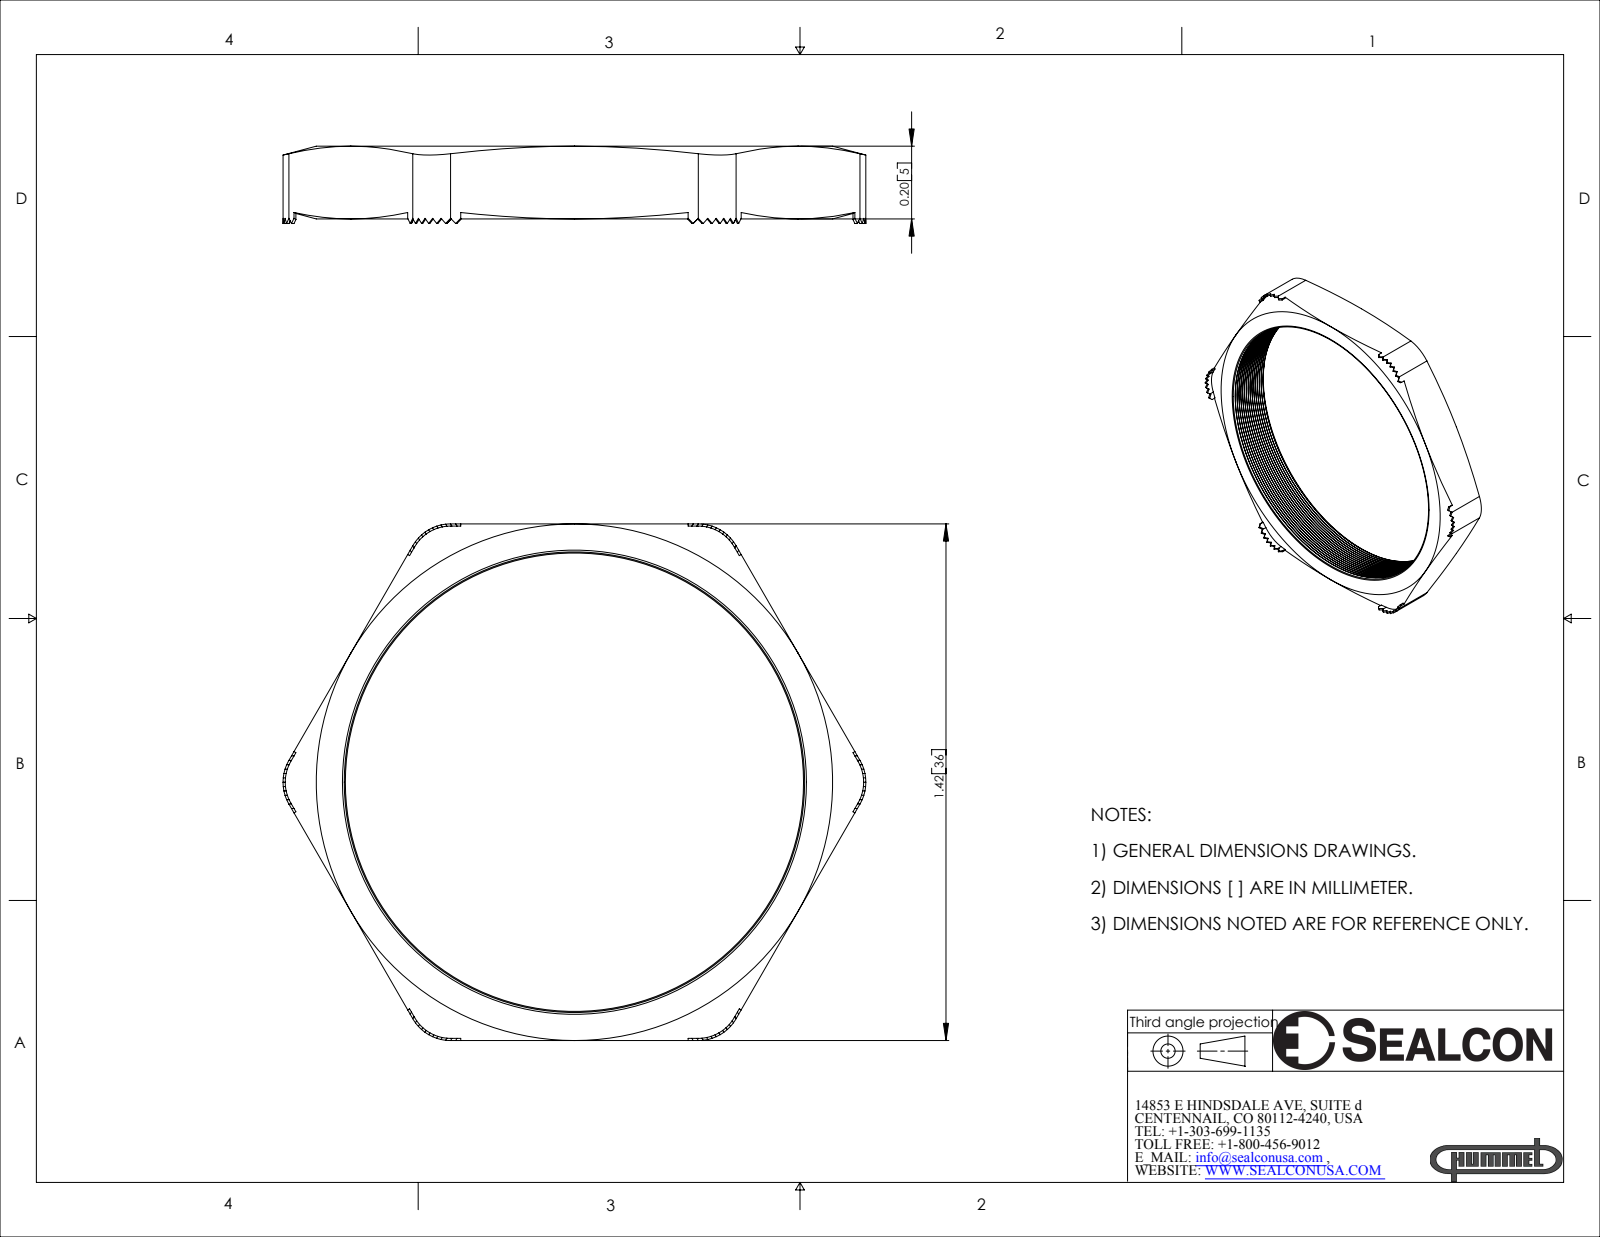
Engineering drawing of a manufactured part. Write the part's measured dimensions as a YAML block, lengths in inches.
part_name: "NM-32-BE"
step_written_by: "SolidWorks 2007 (CONFIG_CONTROL_DESIGN)"
units: inches
bodies: {solids: 1, faces: 248, planar: 116, cylindrical: 46, other: 86}
overall_size: [1.603, 1.42, 0.213]
volume: 0.093
surface_area: 3.454
round_holes:
  - {diameter: 1.26, count: 1}
partial_cylinders:
  - {radius: 0.114, count: 6}
  - {radius: 0.12, count: 6}
face_to_face_distances: [1.42, 0.2, 1.414, 0.019, 0.037, 1.408, 0.055, 0.037, 0.018, 0.074]
